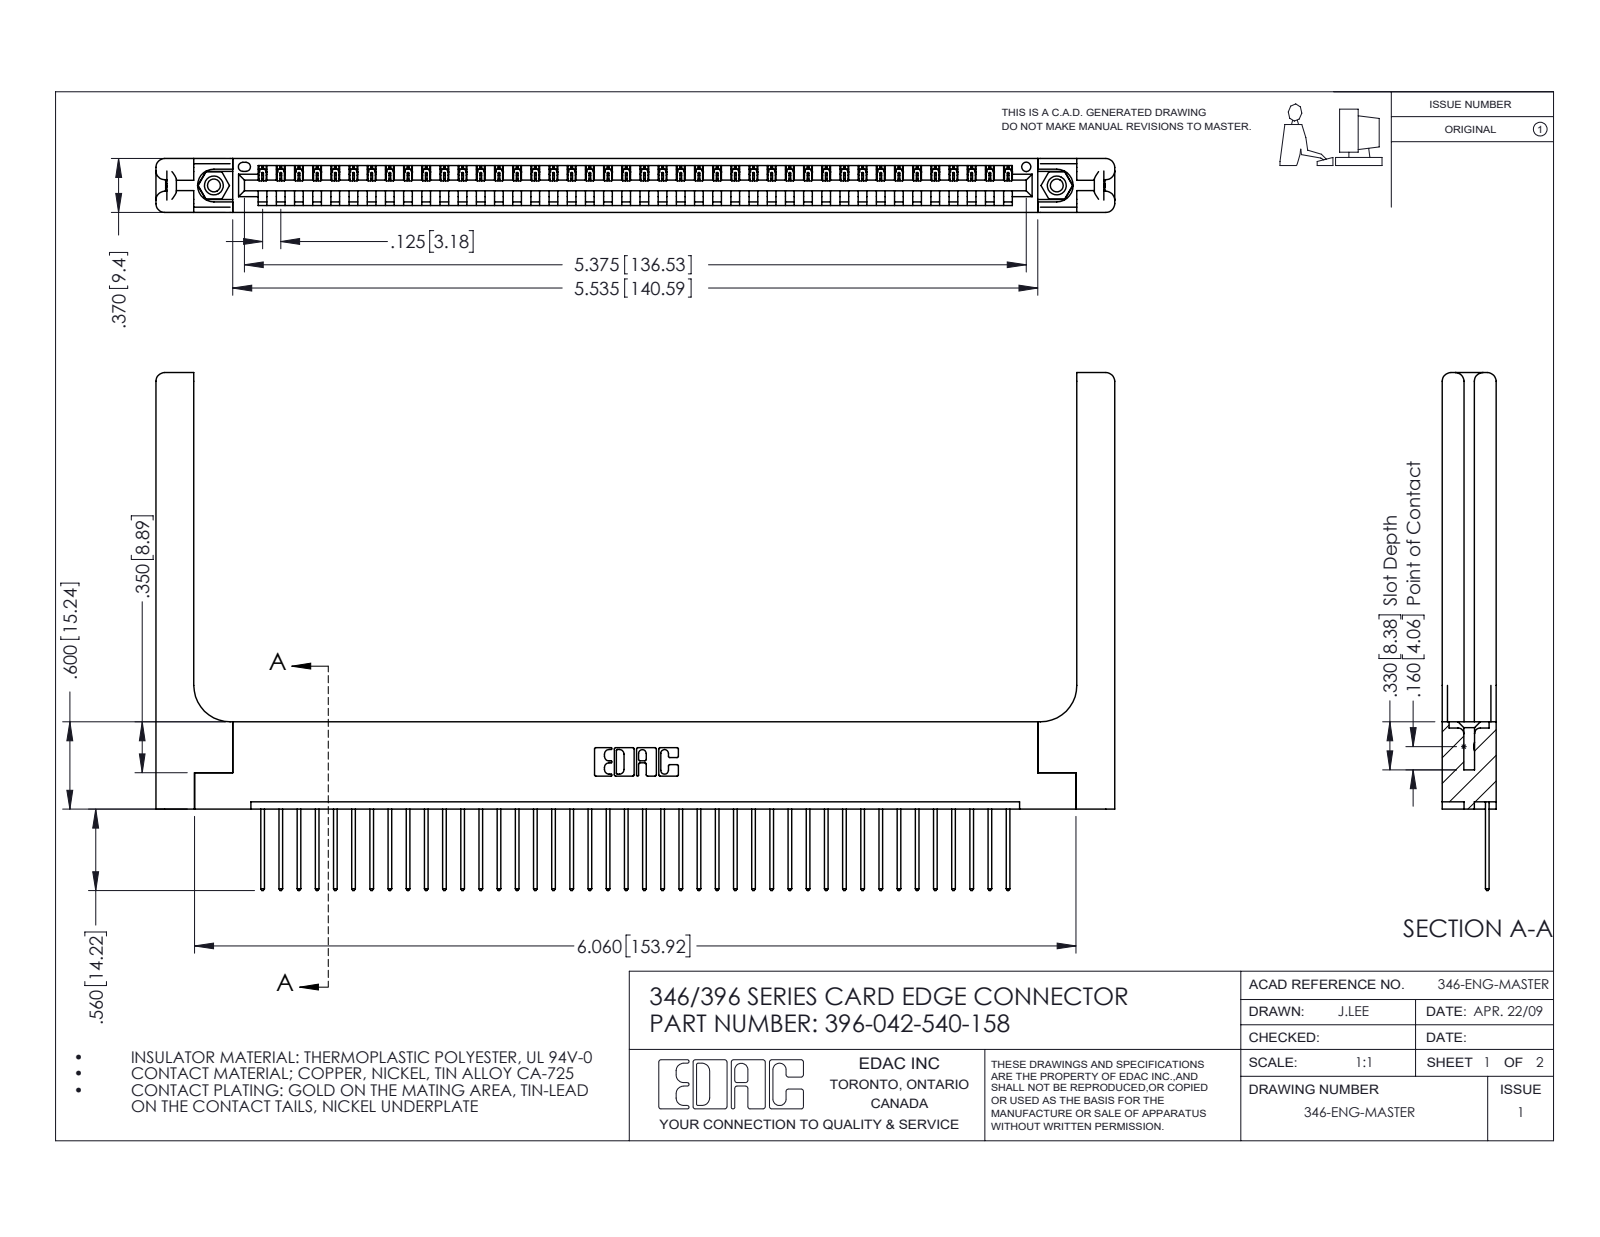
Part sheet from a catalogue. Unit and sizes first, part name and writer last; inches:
Units: inches
Overall size (bounding box): 6.591 × 3.56 × 0.37
Round holes (diameter × count): ⌀0.089 ×2, ⌀0.125 ×2, ⌀0.156 ×2, ⌀0.064 ×1
Round bosses / shafts (diameter × count): ⌀0.155 ×2
Partial cylindrical surfaces — rounded edges, fillets, slot ends (radius × count): R0.006 ×84, R0.01 ×84, R0.01 ×22, R0.06 ×16, R0.007 ×6, R0.031 ×6, R0.026 ×3, R0.03 ×2
Main face-to-face distances: 0.37, 0.048, 0.322, 0.072, 0.148, 0.15, 0.25, 0.298, 0.025, 0.222
Hole centre spacings: 0.246, 5.586, 5.795
Volume: 1.44 in³ · Surface area: 39.81 in²
Bodies: 47 solids, 2814 faces (1904 planar, 850 cylindrical, 60 other)
Part name (STEP PRODUCT): 346 Part_Flush Mounting Lugs - 0.156 Dia-TH; 345-292-001_345-293-140; 345-250-001_345-250-001-102; 396-042-540-158 (+1 more)
STEP written by: SolidWorks 2016 (CONFIG_CONTROL_DESIGN)
